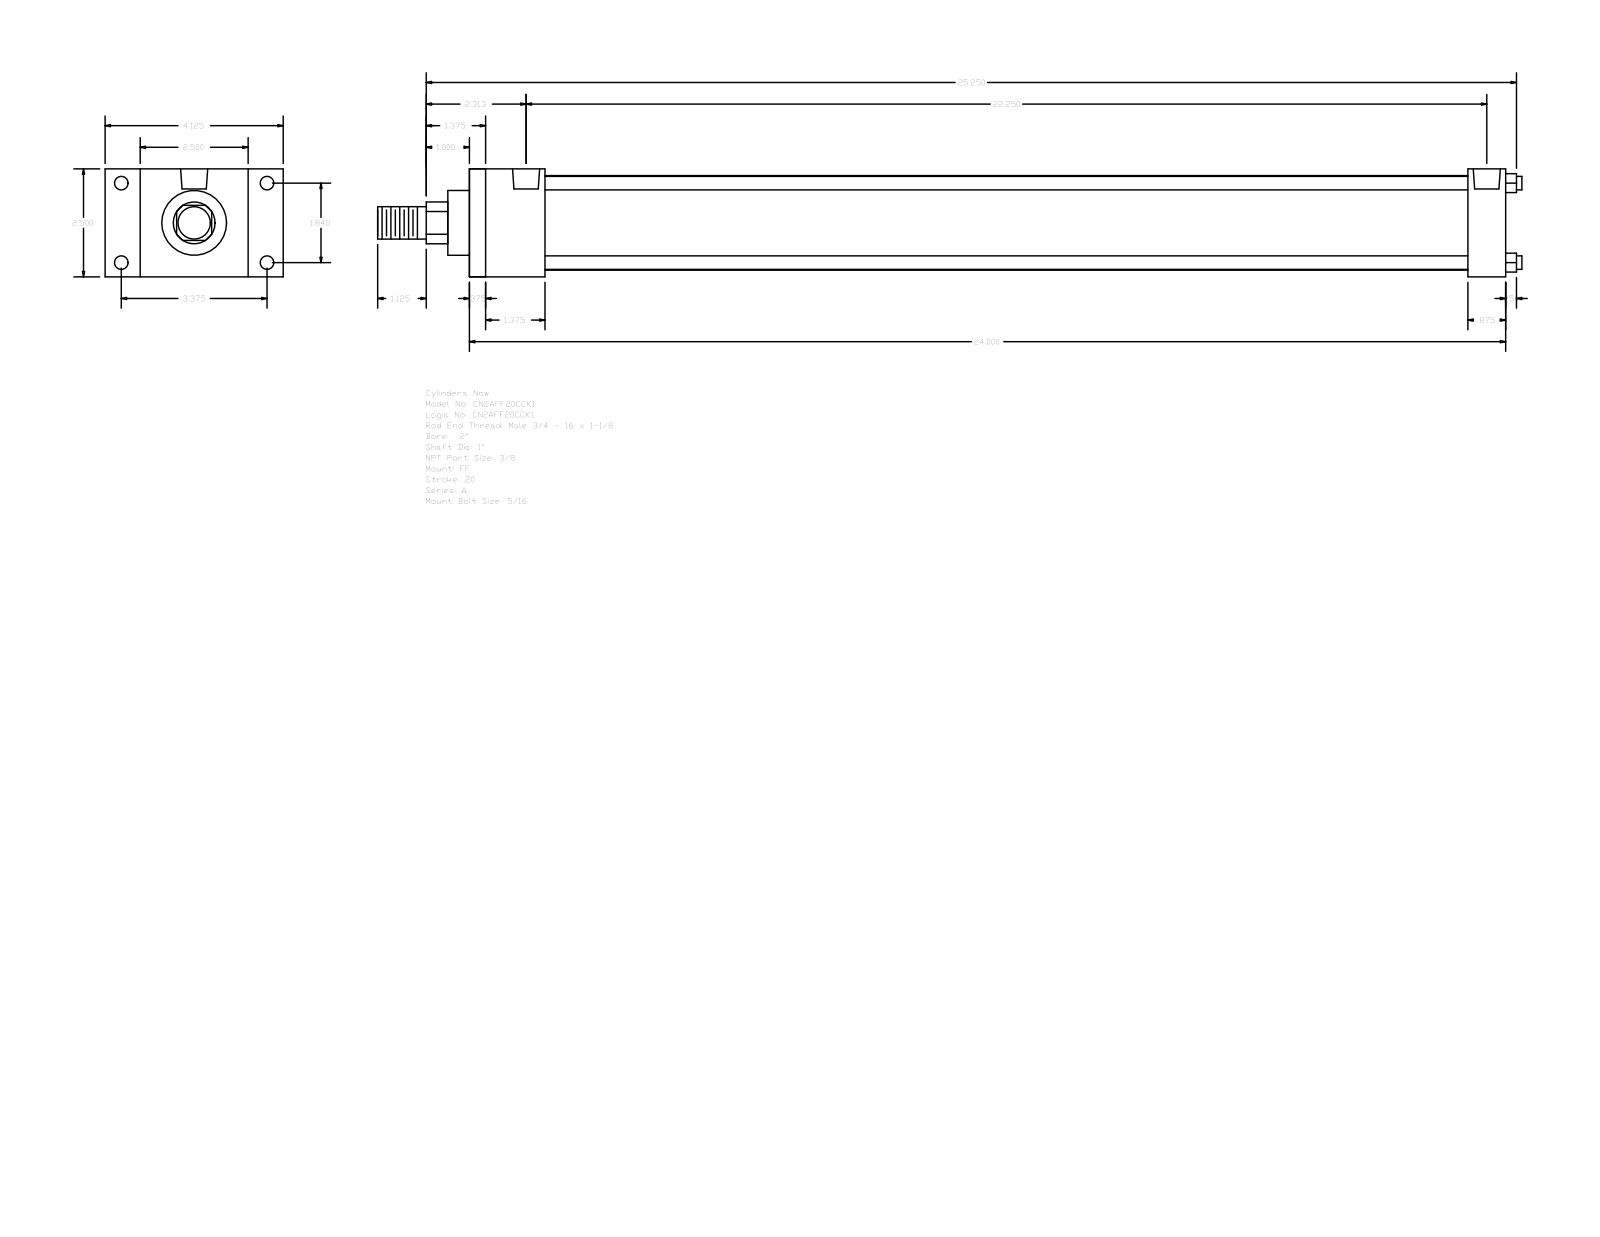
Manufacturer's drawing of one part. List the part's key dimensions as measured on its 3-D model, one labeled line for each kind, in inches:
Part name (STEP PRODUCT): A_FF__0200_1
STEP written by: GSSL Pune (CONFIG_CONTROL_DESIGN)
Units: inches
Bodies: 0 solids, 92 faces (64 planar, 28 cylindrical, 0 other)
Overall size (bounding box): 26.5 × 4.125 × 2.5
Round holes (diameter × count): ⌀0.219 ×4, ⌀0.313 ×4, ⌀0.627 ×2
Round bosses / shafts (diameter × count): ⌀0.313 ×4, ⌀2.19 ×1, ⌀1.5 ×1, ⌀1 ×1, ⌀0.75 ×1
Partial cylindrical surfaces — rounded edges, fillets, slot ends (radius × count): R0.484 ×1
Main face-to-face distances: 2.5, 24, 0.375, 23.625, 0.813, 1.75, 23.125, 1.375, 22.75, 21.375
Hole centre spacings: 1.84, 3.375, 3.844, 22.031, 0.063, 0.157, 22.093, 22.187
